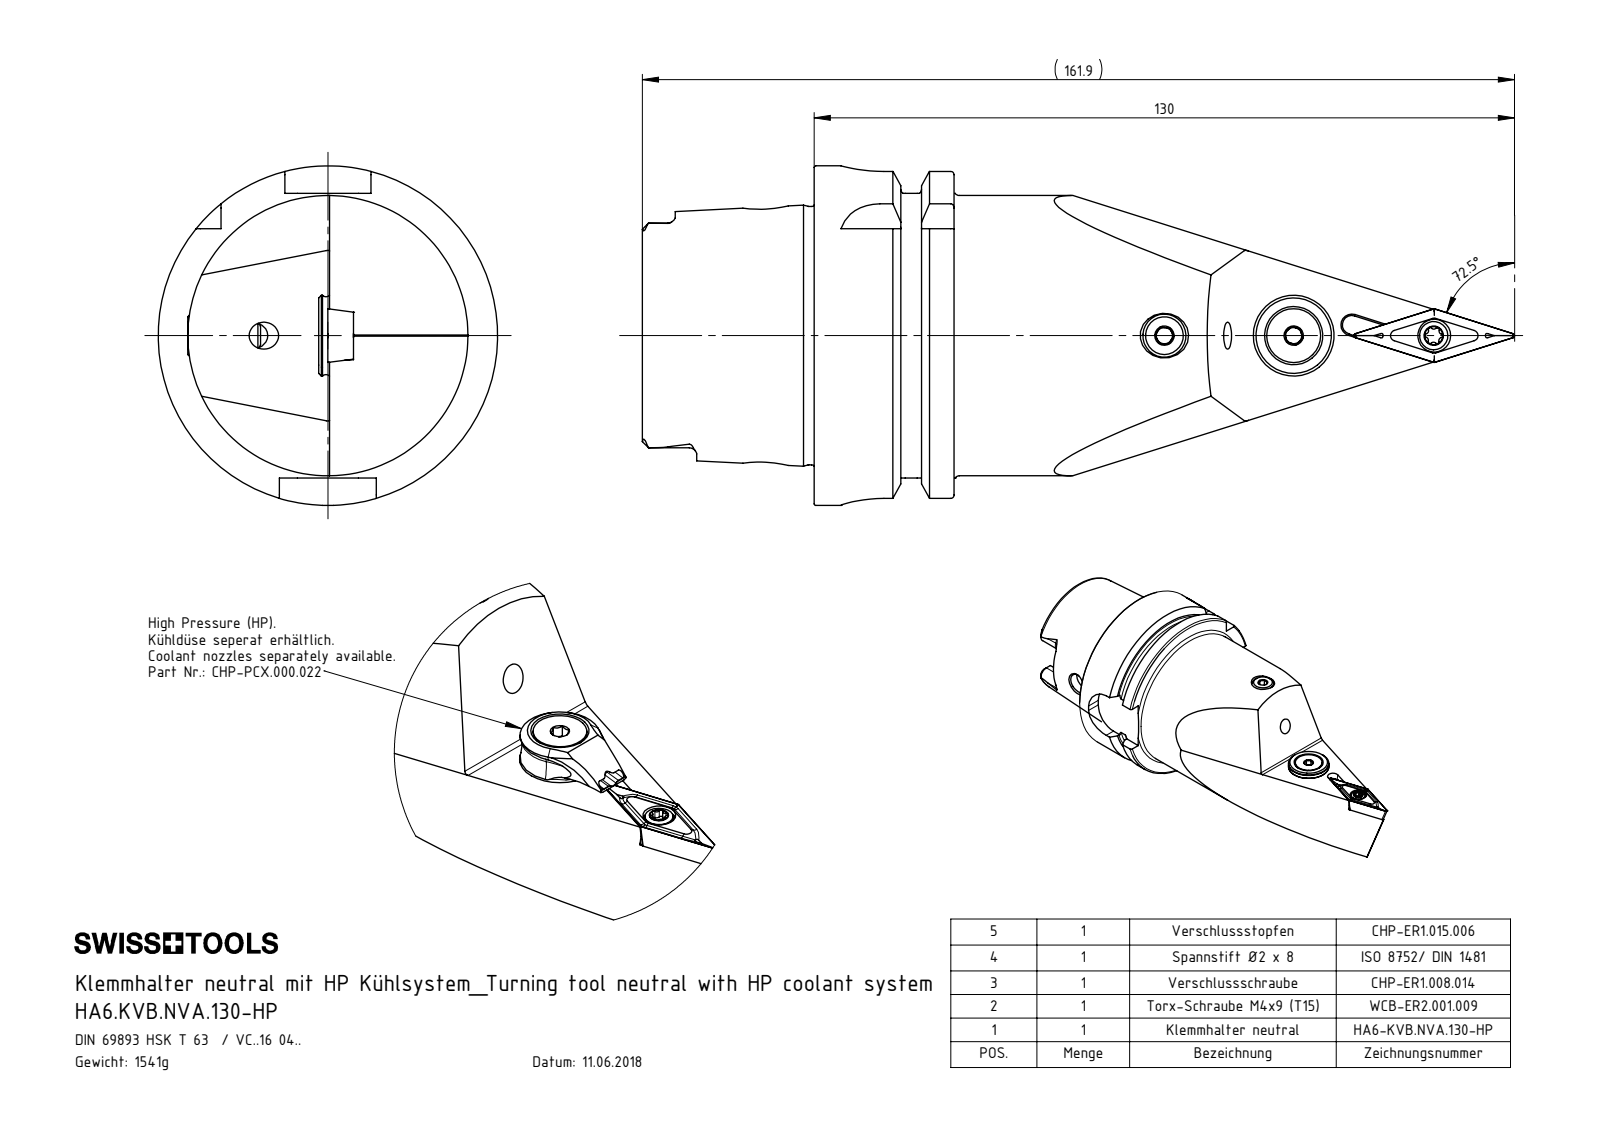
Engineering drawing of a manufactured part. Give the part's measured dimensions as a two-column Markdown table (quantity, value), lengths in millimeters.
| quantity | value |
| --- | --- |
| part name | HA6-KVB.NVA.130-HP_B; DIN 3771 - 13x1; CHP-ER1.008.014_A; WCB-ER2.001.009_A (+6 more) |
| STEP written by | SolidWorks 2017 (AUTOMOTIVE_DESIGN) |
| units | millimeters |
| bodies | 8 solids, 305 faces (118 planar, 73 cylindrical, 114 other) |
| overall size | 161.9 × 63 × 63 |
| volume | 196 292 mm³ |
| surface area | 37 799 mm² |
| round holes (diameter × count) | 5 × 3, 4.2 × 2, 1.2 × 1, 2 × 1, 2.5 × 1, 3 × 1, 3.3 × 1, 4.4 × 1, 5.2 × 1, 6.1 × 1, 7 × 1, 7.5 × 1 |
| round bosses / shafts (diameter × count) | 63 × 1, 54.95 × 1, 52 × 1, 47.94 × 1, 15 × 1, 13.4 × 1, 10 × 1, 8 × 1 |
| partial cylindrical surfaces (radius × count) | 0.34 × 6, 0.59 × 6, 1.4 × 6, 8 × 4, 2.82 × 2, 2.88 × 2, 0.8 × 1, 1.75 × 1 |
| main face-to-face distances | 25.95, 16, 9.95, 31.9, 41.85, 57.85, 52.8, 21.8, 11.85, 4.5 |
| hole center spacings | 4.5, 22.67, 22.77, 24, 25.99, 26.09, 27.65, 49.99 |
